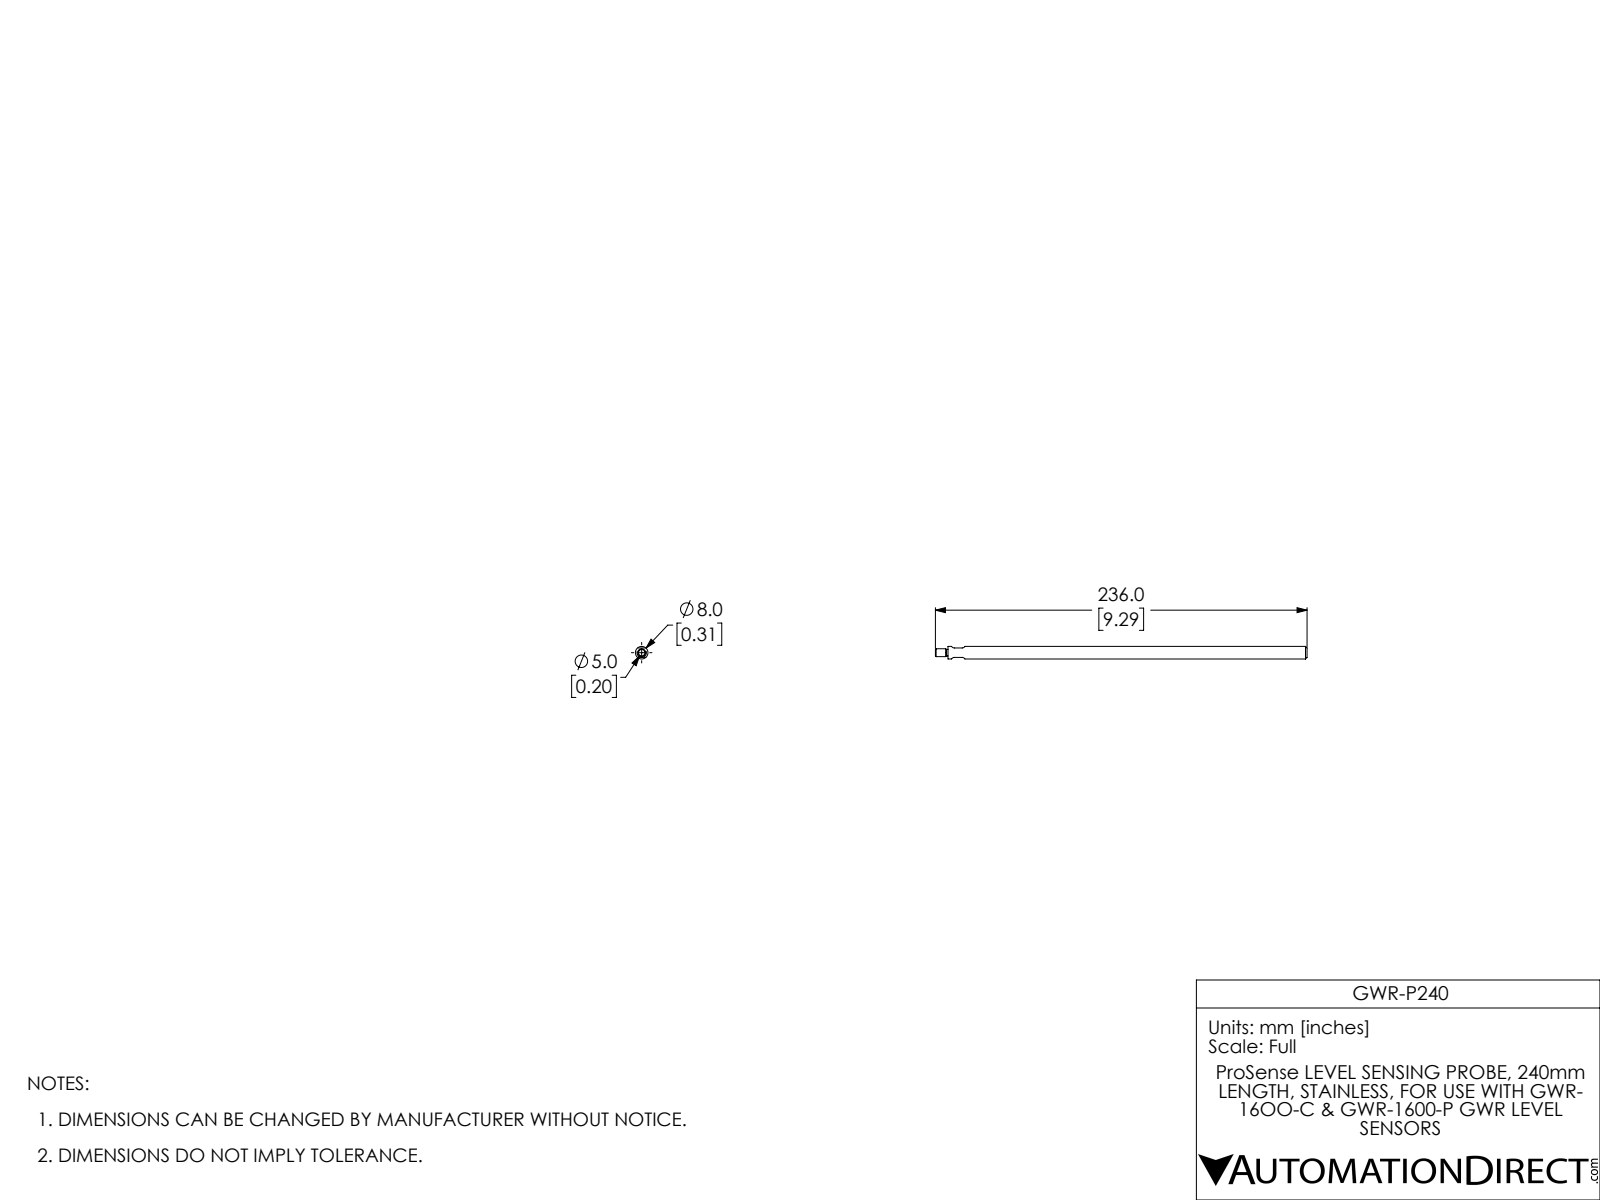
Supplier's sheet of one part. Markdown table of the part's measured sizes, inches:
| quantity | value |
| --- | --- |
| part name | GWR-P240 |
| STEP written by | SolidWorks 2017 (AUTOMOTIVE_DESIGN) |
| units | inches |
| bodies | 1 solid, 21 faces (5 planar, 10 cylindrical, 6 other) |
| overall size | 9.291 × 0.315 × 0.315 |
| volume | 0.704 in³ |
| surface area | 9.206 in² |
| round bosses / shafts (diameter × count) | 0.315 × 1, 0.197 × 1, 0.161 × 1 |
| partial cylindrical surfaces (radius × count) | 0.079 × 4 |
| main face-to-face distances | 8.976, 0.236, 9.291, 0.315 |
